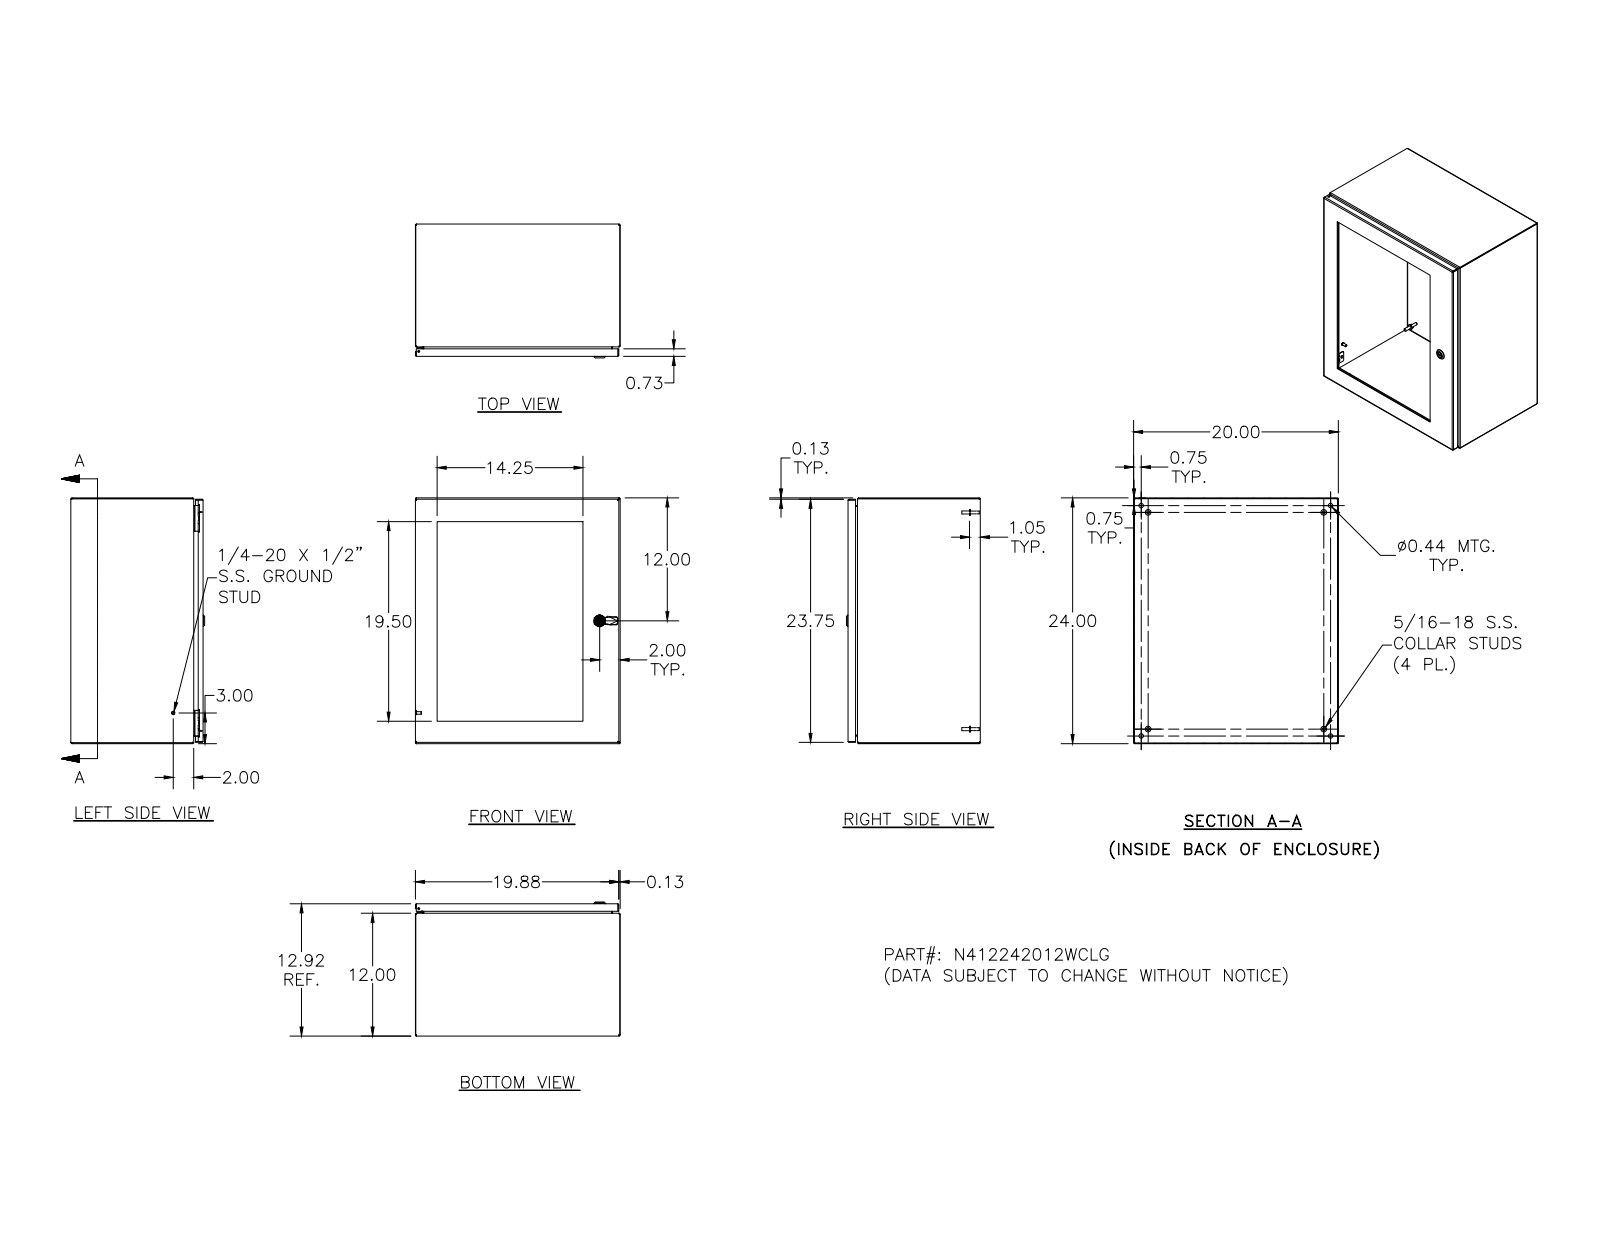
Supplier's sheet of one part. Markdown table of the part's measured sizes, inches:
| quantity | value |
| --- | --- |
| part name | N412242012WCLG |
| STEP written by | SolidWorks 2018 (AUTOMOTIVE_DESIGN) |
| units | inches |
| bodies | 73 solids, 2083 faces (775 planar, 625 cylindrical, 683 other) |
| overall size | 24 × 20 × 13.075 |
| volume | 225.8 in³ |
| surface area | 4 675 in² |
| round holes (diameter × count) | 0.156 × 20, 0.281 × 18, 0.188 × 5, 0.093 × 4, 0.152 × 4, 0.167 × 4, 0.172 × 4, 0.437 × 4, 0.187 × 1, 0.197 × 1, 0.315 × 1, 0.394 × 1 |
| round bosses / shafts (diameter × count) | 0.337 × 18, 0.19 × 18, 0.25 × 10, 0.563 × 4, 0.36 × 4, 0.32 × 4, 0.3 × 4, 0.275 × 4 |
| partial cylindrical surfaces (radius × count) | 0.031 × 34, 0.012 × 30, 0.05 × 26, 0.105 × 24, 0.016 × 18, 0.125 × 16, 0.02 × 13, 0.032 × 8 |
| main face-to-face distances | 0.074, 12.843, 19.926, 12.769, 23.926, 0.25, 12.593, 12.519, 20, 19.852 |
| hole center spacings | 4, 8, 16.008, 12, 17.443, 20, 21.132, 15.5 |
